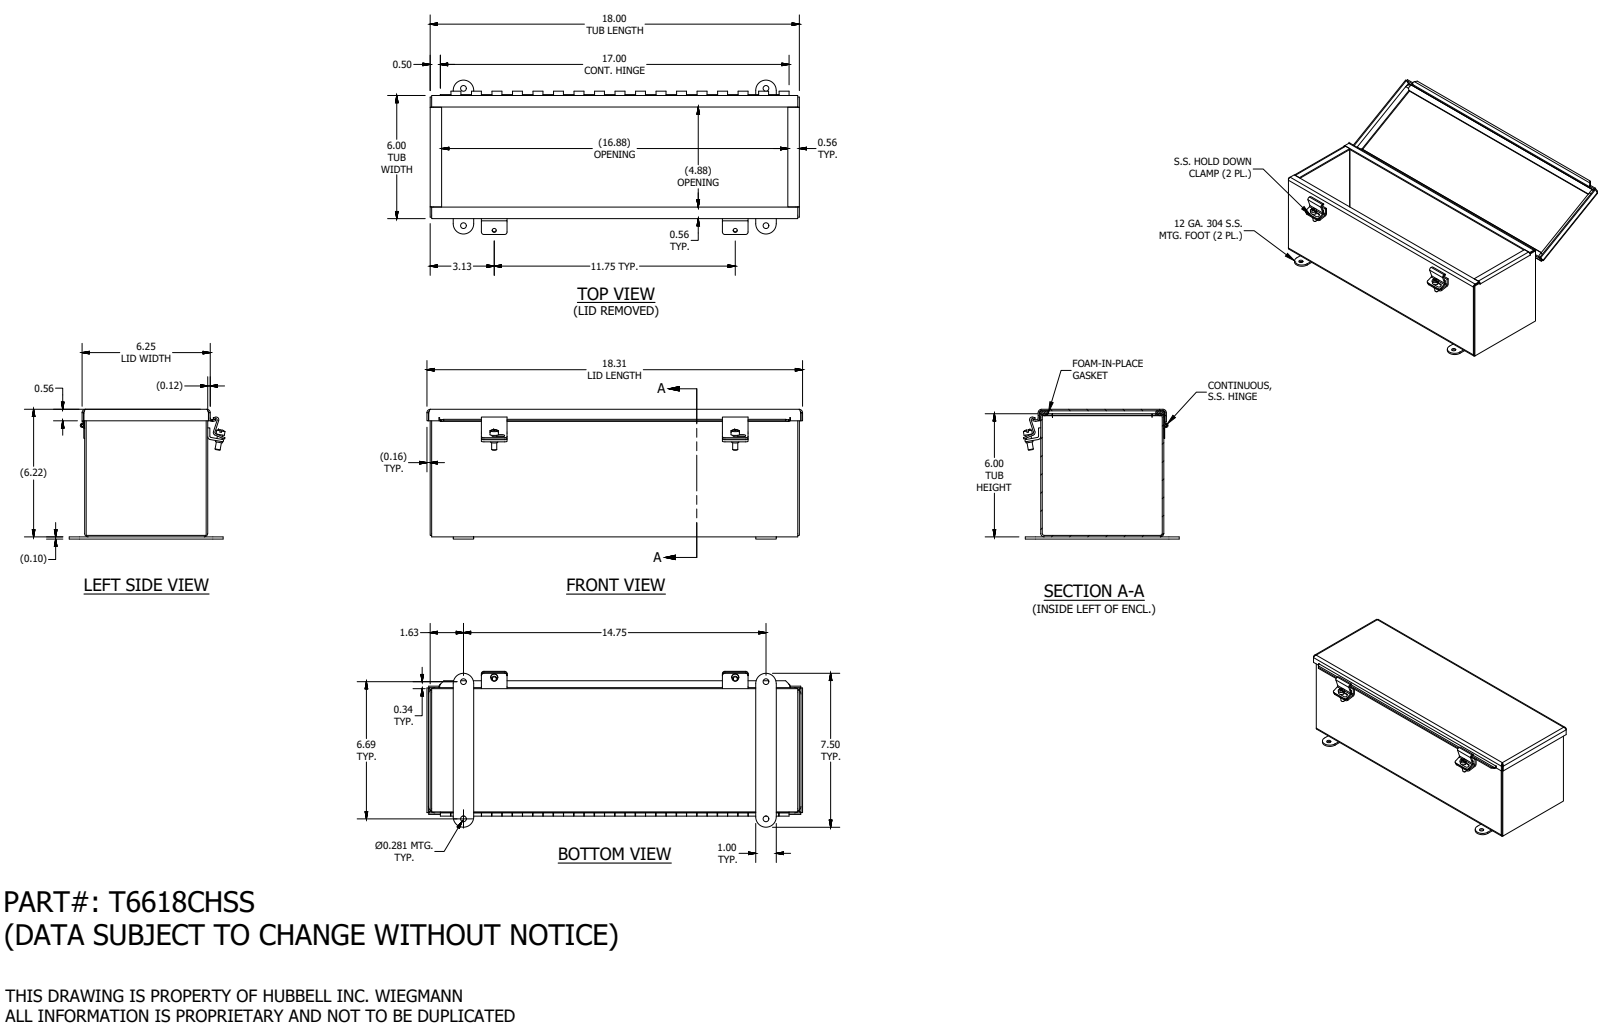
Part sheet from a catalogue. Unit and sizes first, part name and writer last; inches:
Units: inches
Overall size (bounding box): 18.313 × 7.598 × 6.322
Round holes (diameter × count): ⌀0.11 ×4, ⌀0.281 ×4, ⌀0.196 ×2, ⌀0.116 ×1
Round bosses / shafts (diameter × count): ⌀0.41 ×2, ⌀0.344 ×2, ⌀0.25 ×2, ⌀0.2 ×1, ⌀0.1 ×1
Partial cylindrical surfaces — rounded edges, fillets, slot ends (radius × count): R0.094 ×11, R0.168 ×11, R0.085 ×8, R0.125 ×8, R0.133 ×4, R0.242 ×4, R0.5 ×4, R0.063 ×3
Main face-to-face distances: 0.074, 5.926, 6.144, 6, 5.852, 6.218, 6.07, 17.926, 0.218, 17.852
Hole centre spacings: 0.75, 6.687, 11.75, 14.75, 16.195, 11, 11.75, 12.5
Volume: 47.84 in³ · Surface area: 1 270 in²
Bodies: 16 solids, 466 faces (281 planar, 153 cylindrical, 32 other)
Part name (STEP PRODUCT): T6618CHSS
STEP written by: SolidWorks 2019 (AUTOMOTIVE_DESIGN)
